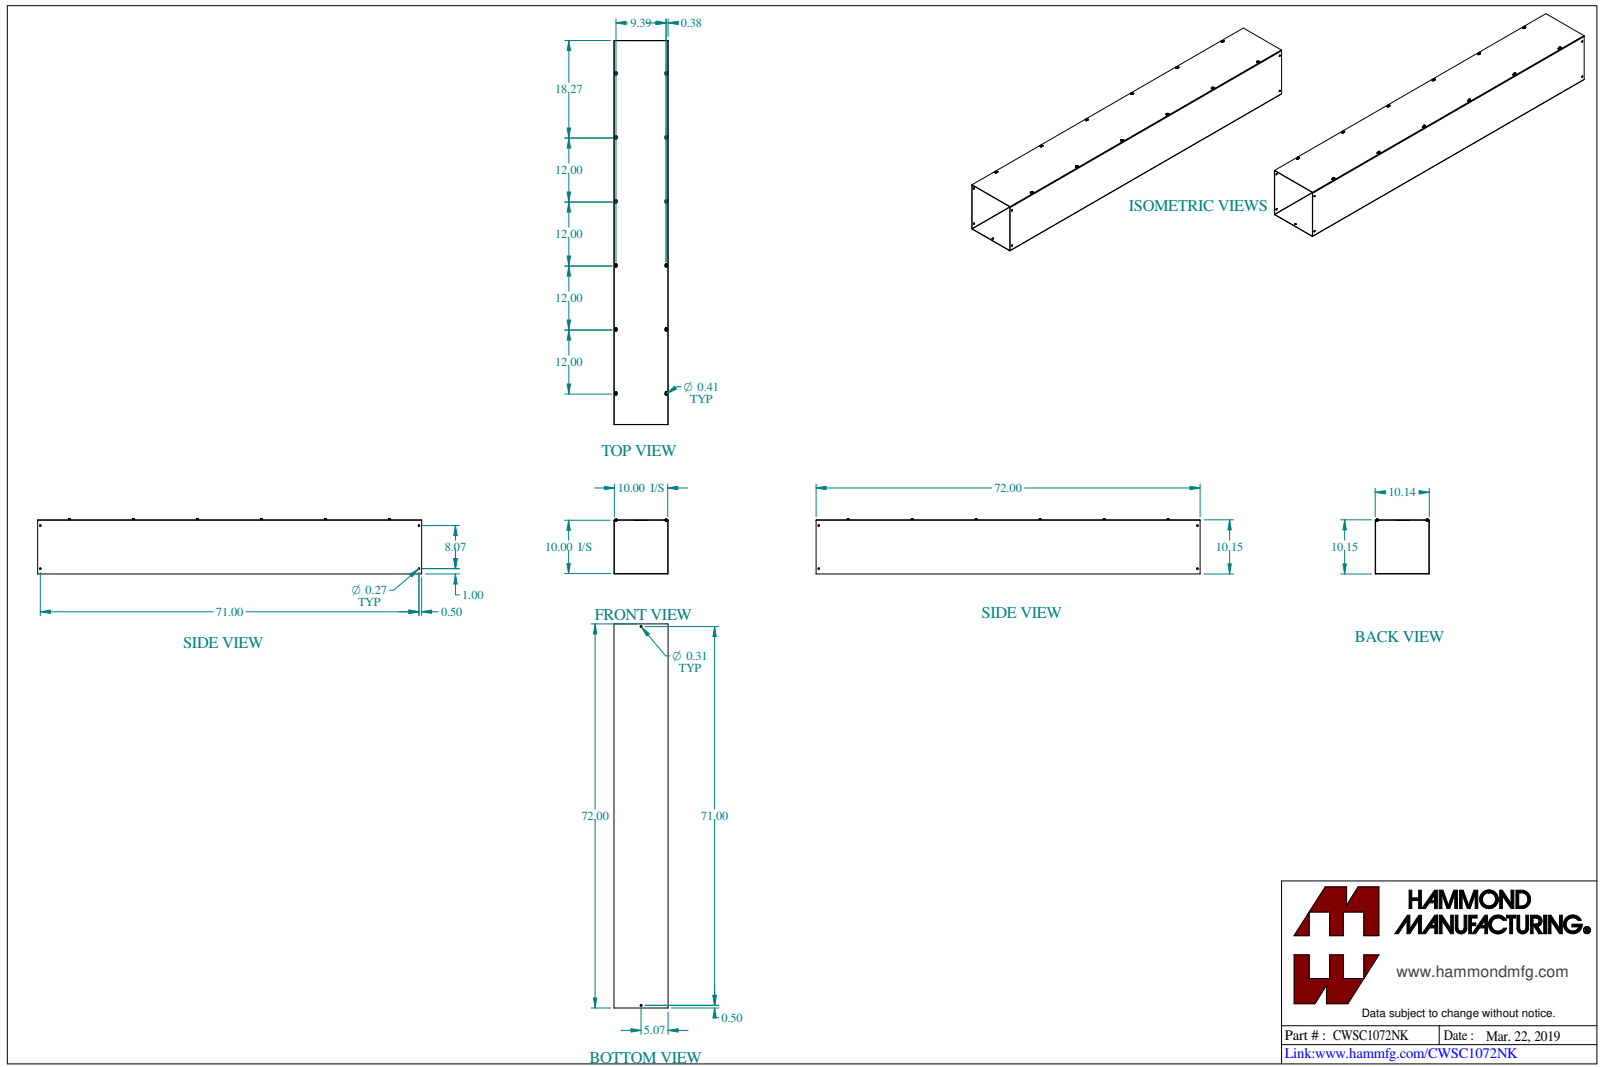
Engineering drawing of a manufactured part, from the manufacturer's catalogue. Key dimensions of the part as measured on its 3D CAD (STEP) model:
Part name (STEP PRODUCT): CWSC1072NK
STEP written by: SolidWorks 2023 (CONFIG_CONTROL_DESIGN)
Units: inches
Bodies: 14 solids, 428 faces (208 planar, 148 cylindrical, 72 other)
Overall size (bounding box): 72 × 10.325 × 10.144
Volume: 219.1 in³ · Surface area: 5 996 in²
Round holes (diameter × count): ⌀0.177 ×12, ⌀0.266 ×4, ⌀0.313 ×2
Round bosses / shafts (diameter × count): ⌀0.375 ×12, ⌀0.19 ×12
Partial cylindrical surfaces — rounded edges, fillets, slot ends (radius × count): R0.125 ×12, R0.203 ×12, R0.036 ×4, R0.108 ×4
Main face-to-face distances: 0.072, 10.072, 10, 0.078, 10.15, 10.078, 10.144, 9.928, 0.15, 0.031
Hole centre spacings: 12, 15.239, 24, 25.773, 9.394, 36, 37.206, 7.233
